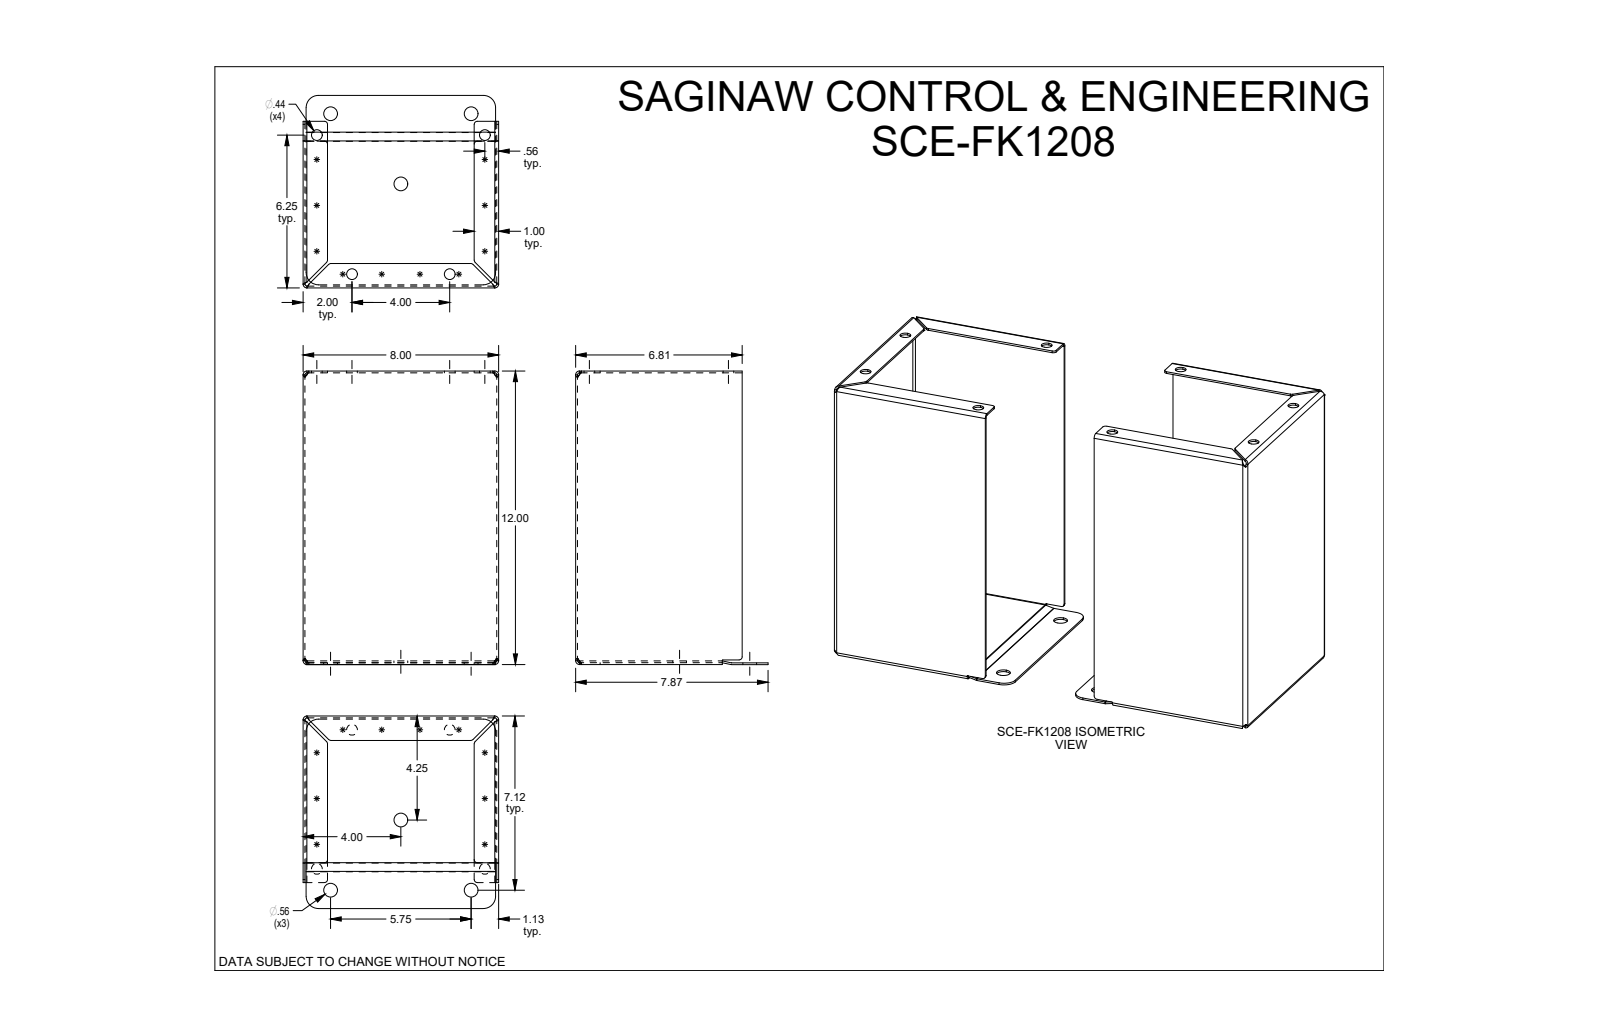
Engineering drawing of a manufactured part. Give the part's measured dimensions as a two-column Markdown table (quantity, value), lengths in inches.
| quantity | value |
| --- | --- |
| part name | SCE-FK1208 |
| STEP written by | SolidWorks 2019 (CONFIG_CONTROL_DESIGN) |
| units | inches |
| bodies | 4 solids, 222 faces (96 planar, 94 cylindrical, 32 other) |
| overall size | 18.5 × 12.005 × 8 |
| volume | 51.95 in³ |
| surface area | 1 403 in² |
| round holes (diameter × count) | 0.437 × 8, 0.563 × 6 |
| partial cylindrical surfaces (radius × count) | 0.125 × 19, 0.08 × 12, 0.155 × 12, 0.5 × 8, 0.138 × 4, 0.02 × 2, 0.062 × 2, 0.063 × 2 |
| main face-to-face distances | 0.075, 0.075, 7.925, 18.425, 8, 18.5, 18.35, 7.85, 7.85, 7.925 |
| hole center spacings | 3.976, 4.197, 5.158, 5.866, 6.618, 7.683, 7.869, 8.705 |
